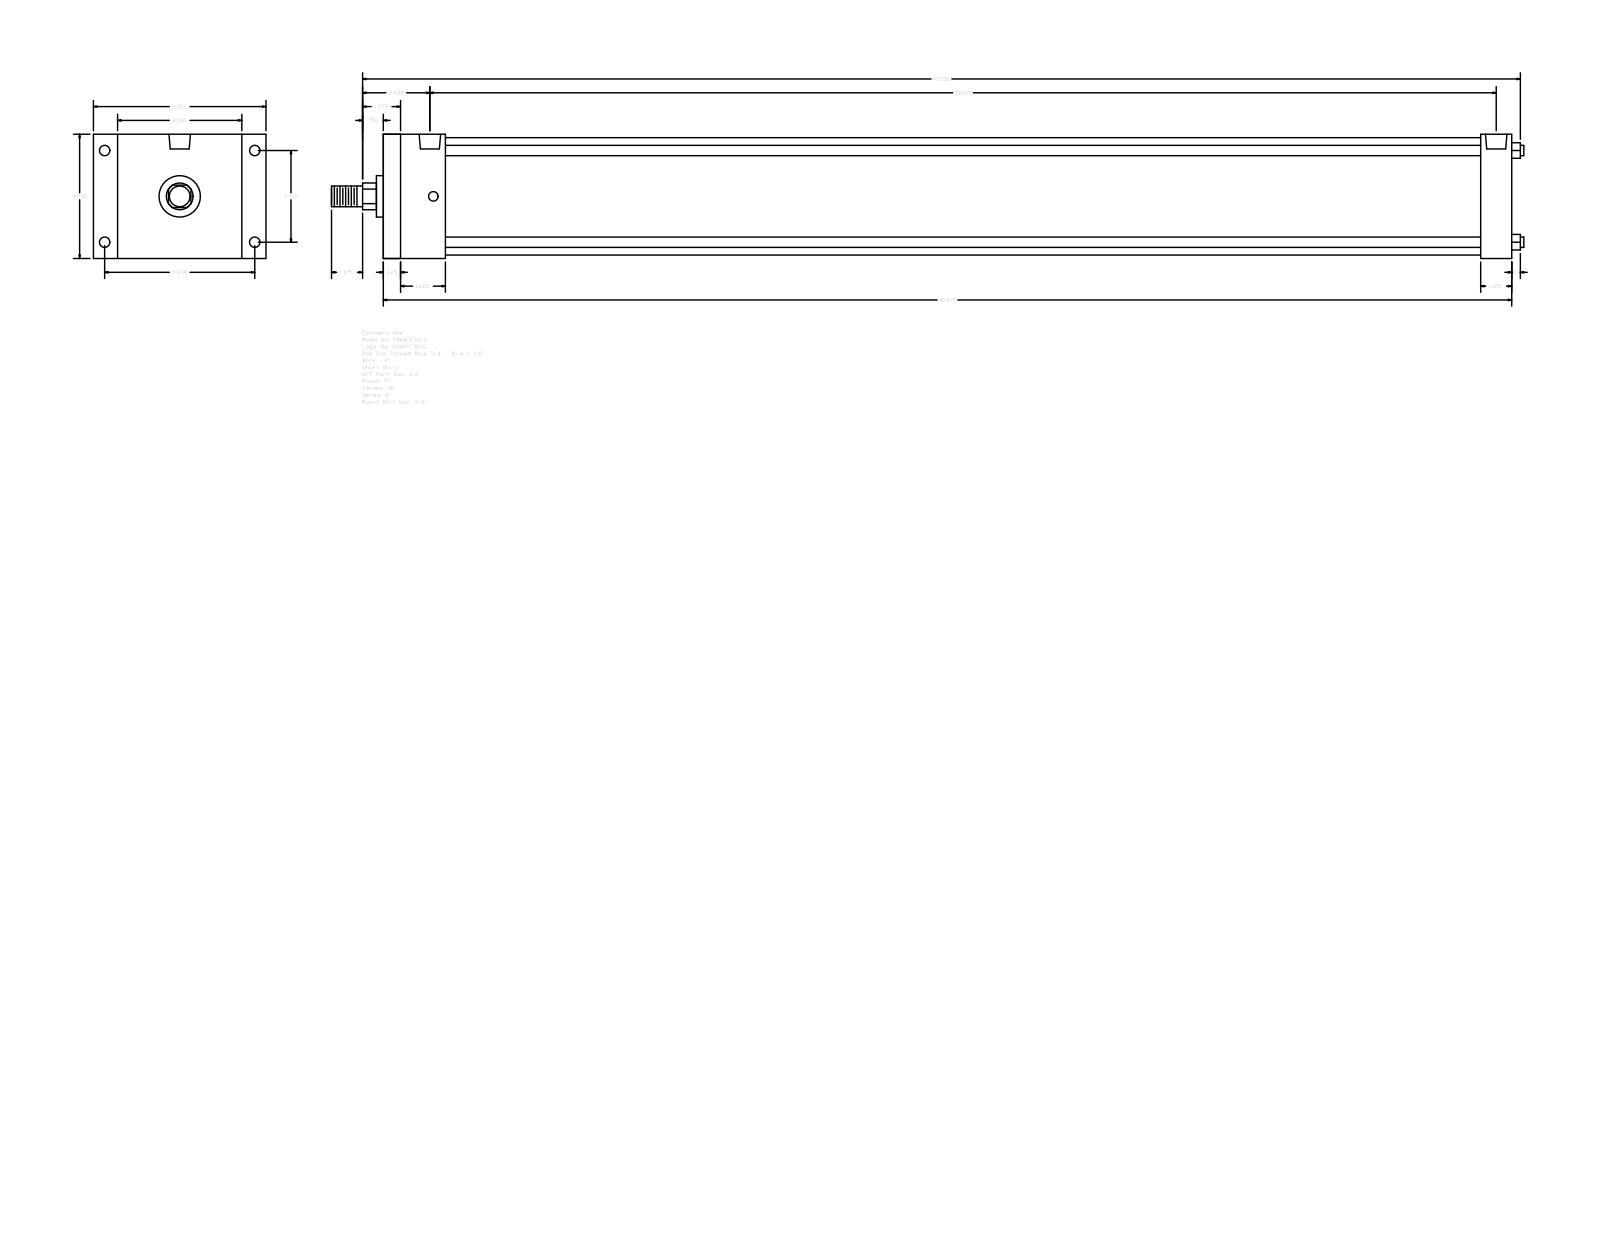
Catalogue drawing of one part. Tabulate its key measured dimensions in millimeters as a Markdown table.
| quantity | value |
| --- | --- |
| part name | A_FF__0400_1 |
| STEP written by | GSSL Pune (CONFIG_CONTROL_DESIGN) |
| units | millimeters |
| bodies | 0 solids, 92 faces (64 planar, 28 cylindrical, 0 other) |
| overall size | 1096.96 × 158.75 × 114.3 |
| round holes (diameter × count) | 8.73 × 4, 9.53 × 4, 19.77 × 2 |
| round bosses / shafts (diameter × count) | 9.53 × 4, 107.95 × 1, 38.1 × 1, 25.4 × 1, 19.05 × 1 |
| partial cylindrical surfaces (radius × count) | 12.29 × 1 |
| main face-to-face distances | 114.3, 1038.23, 15.87, 1022.36, 22.23, 136.53, 1009.65, 993.78, 28.58, 57.15 |
| hole center spacings | 3.18, 84.32, 138.12, 161.82, 974.72, 977.9, 981.08 |
